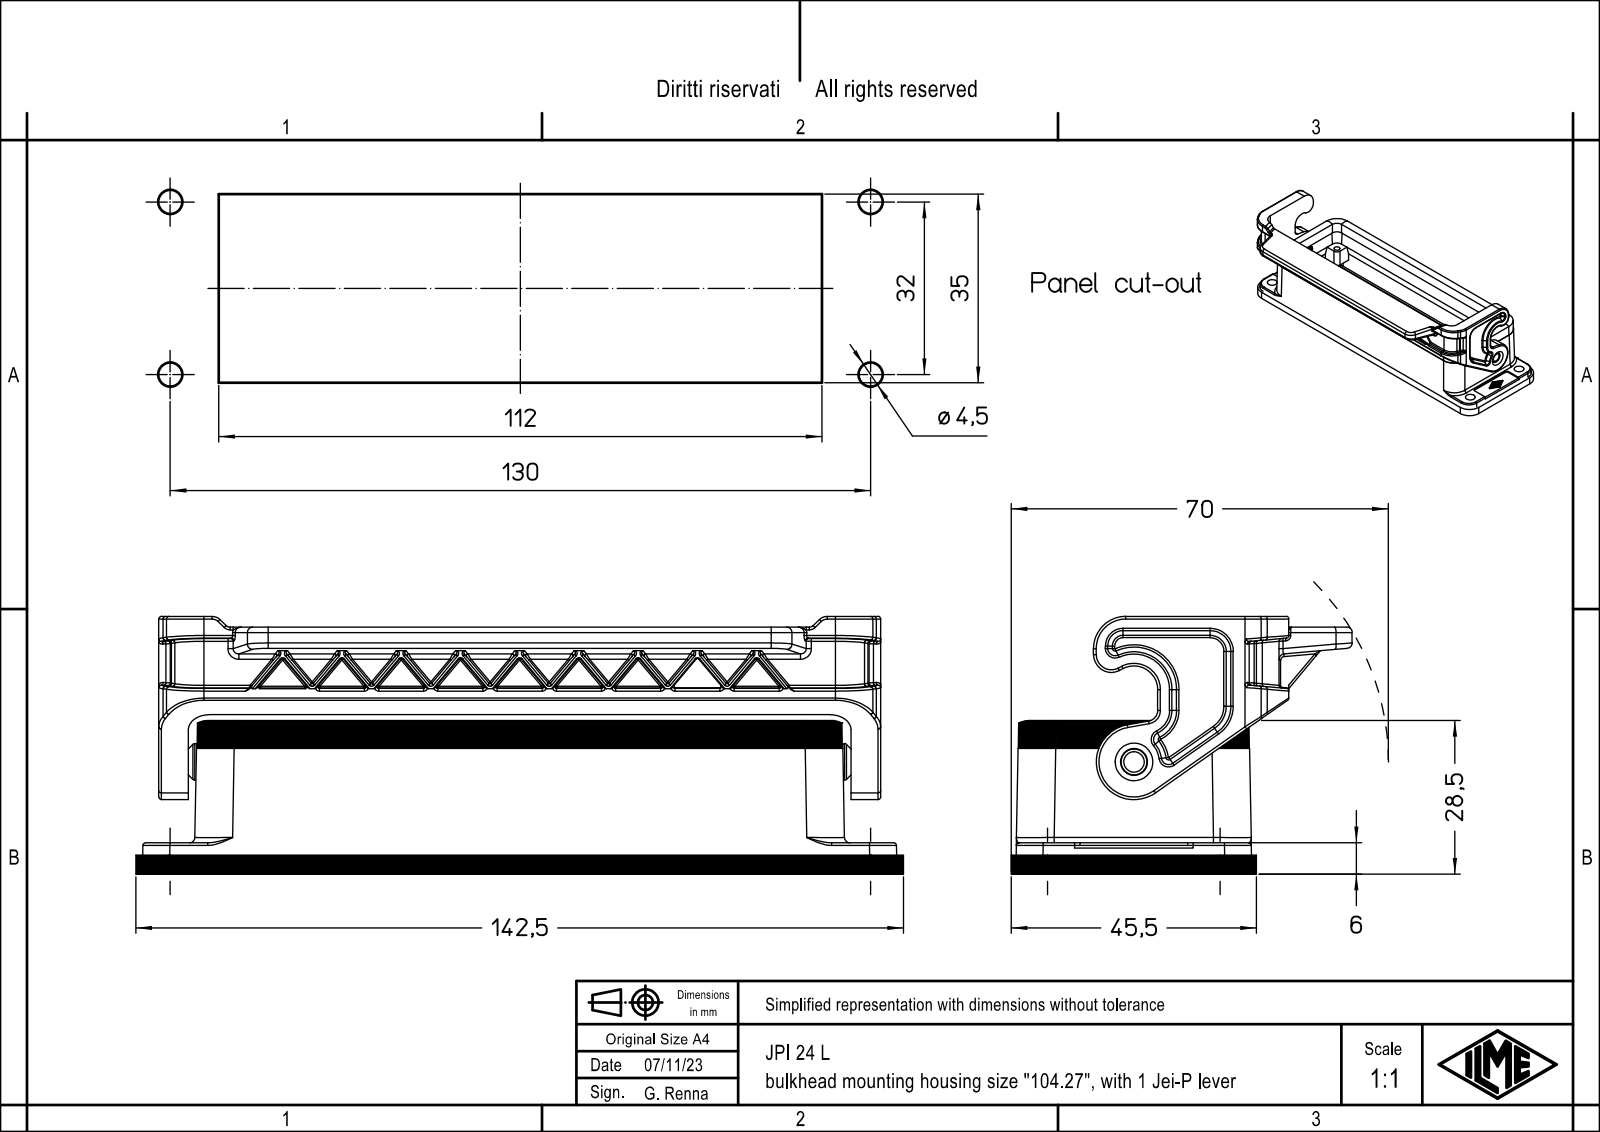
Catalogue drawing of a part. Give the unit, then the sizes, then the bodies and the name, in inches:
Units: inches
Overall size (bounding box): 5.61 × 2.49 × 1.882
Round holes (diameter × count): ⌀0.15 ×4, ⌀0.177 ×4, ⌀0.189 ×1
Round bosses / shafts (diameter × count): ⌀0.268 ×1
Partial cylindrical surfaces — rounded edges, fillets, slot ends (radius × count): R0.012 ×126, R0.02 ×63, R0.157 ×16, R0.007 ×15, R0.039 ×15, R0.079 ×9, R0.276 ×9, R0.118 ×8
Main face-to-face distances: 0.119, 1.803, 0.138, 0.079, 1.594, 1.534, 1.415, 0.117, 1.531, 0.039
Hole centre spacings: 1.26, 5.118, 5.271
Volume: 3.499 in³ · Surface area: 58.75 in²
Bodies: 1 solid, 897 faces (253 planar, 351 cylindrical, 293 other)
Part name (STEP PRODUCT): JPI 24 L
STEP written by: Creo Elements/Direct Modeling 20.1B 02-Apr-2019 (C) Parametric Technology GmbH (AUTOMOTIVE_DESIGN)
